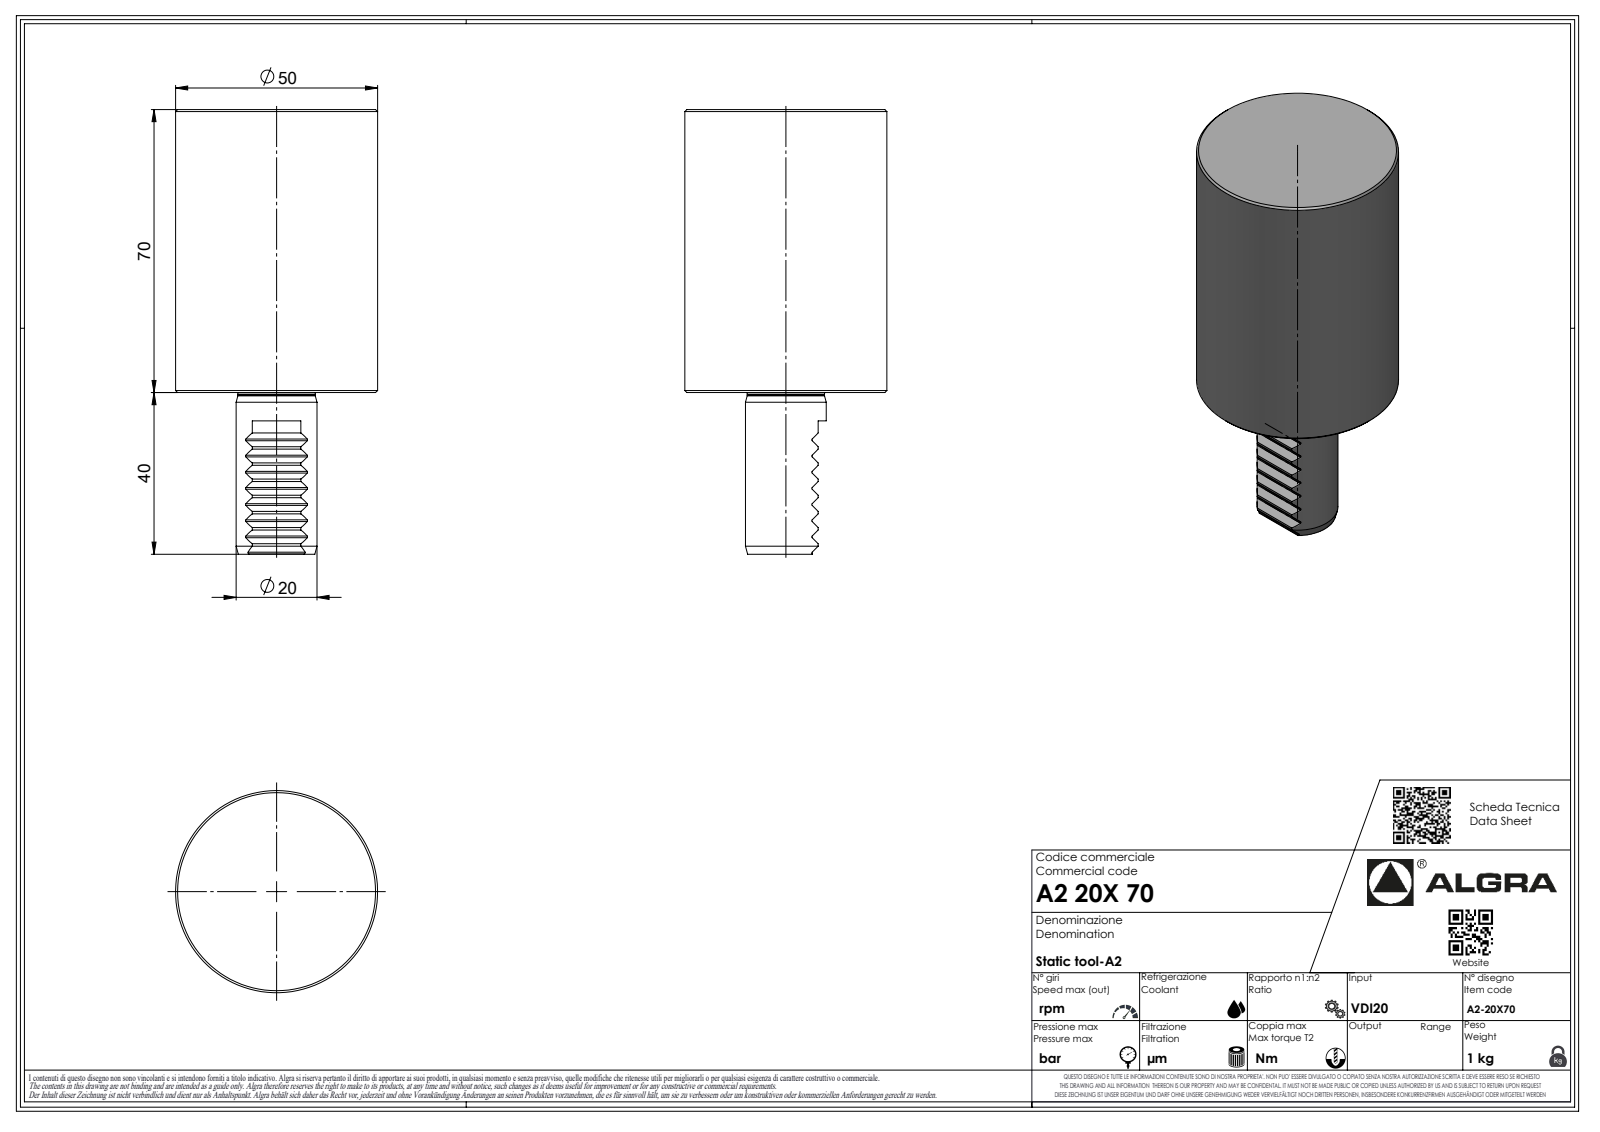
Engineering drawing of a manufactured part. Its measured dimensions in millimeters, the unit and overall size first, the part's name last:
Units: millimetres
Overall size (bounding box): 110 × 50 × 48
Round holes (diameter × count): ⌀2.1 ×1, ⌀9 ×1, ⌀10 ×1
Round bosses / shafts (diameter × count): ⌀50 ×1, ⌀20 ×1, ⌀19.1 ×1, ⌀6.37 ×1, ⌀1.7 ×1
Partial cylindrical surfaces — rounded edges, fillets, slot ends (radius × count): R0.3 ×8, R0.33 ×7, R0.52 ×7, R3.7 ×7, R0.21 ×1
Main face-to-face distances: 70, 2.83, 40, 110, 5.66, 14.14, 8.48, 5.65, 11.31, 8.49
Volume: 146 235 mm³ · Surface area: 17 807 mm²
Bodies: 1 solid, 252 faces (168 planar, 39 cylindrical, 45 other)
Part name (STEP PRODUCT): A220X70
STEP written by: SolidWorks 2023 (AUTOMOTIVE_DESIGN)
